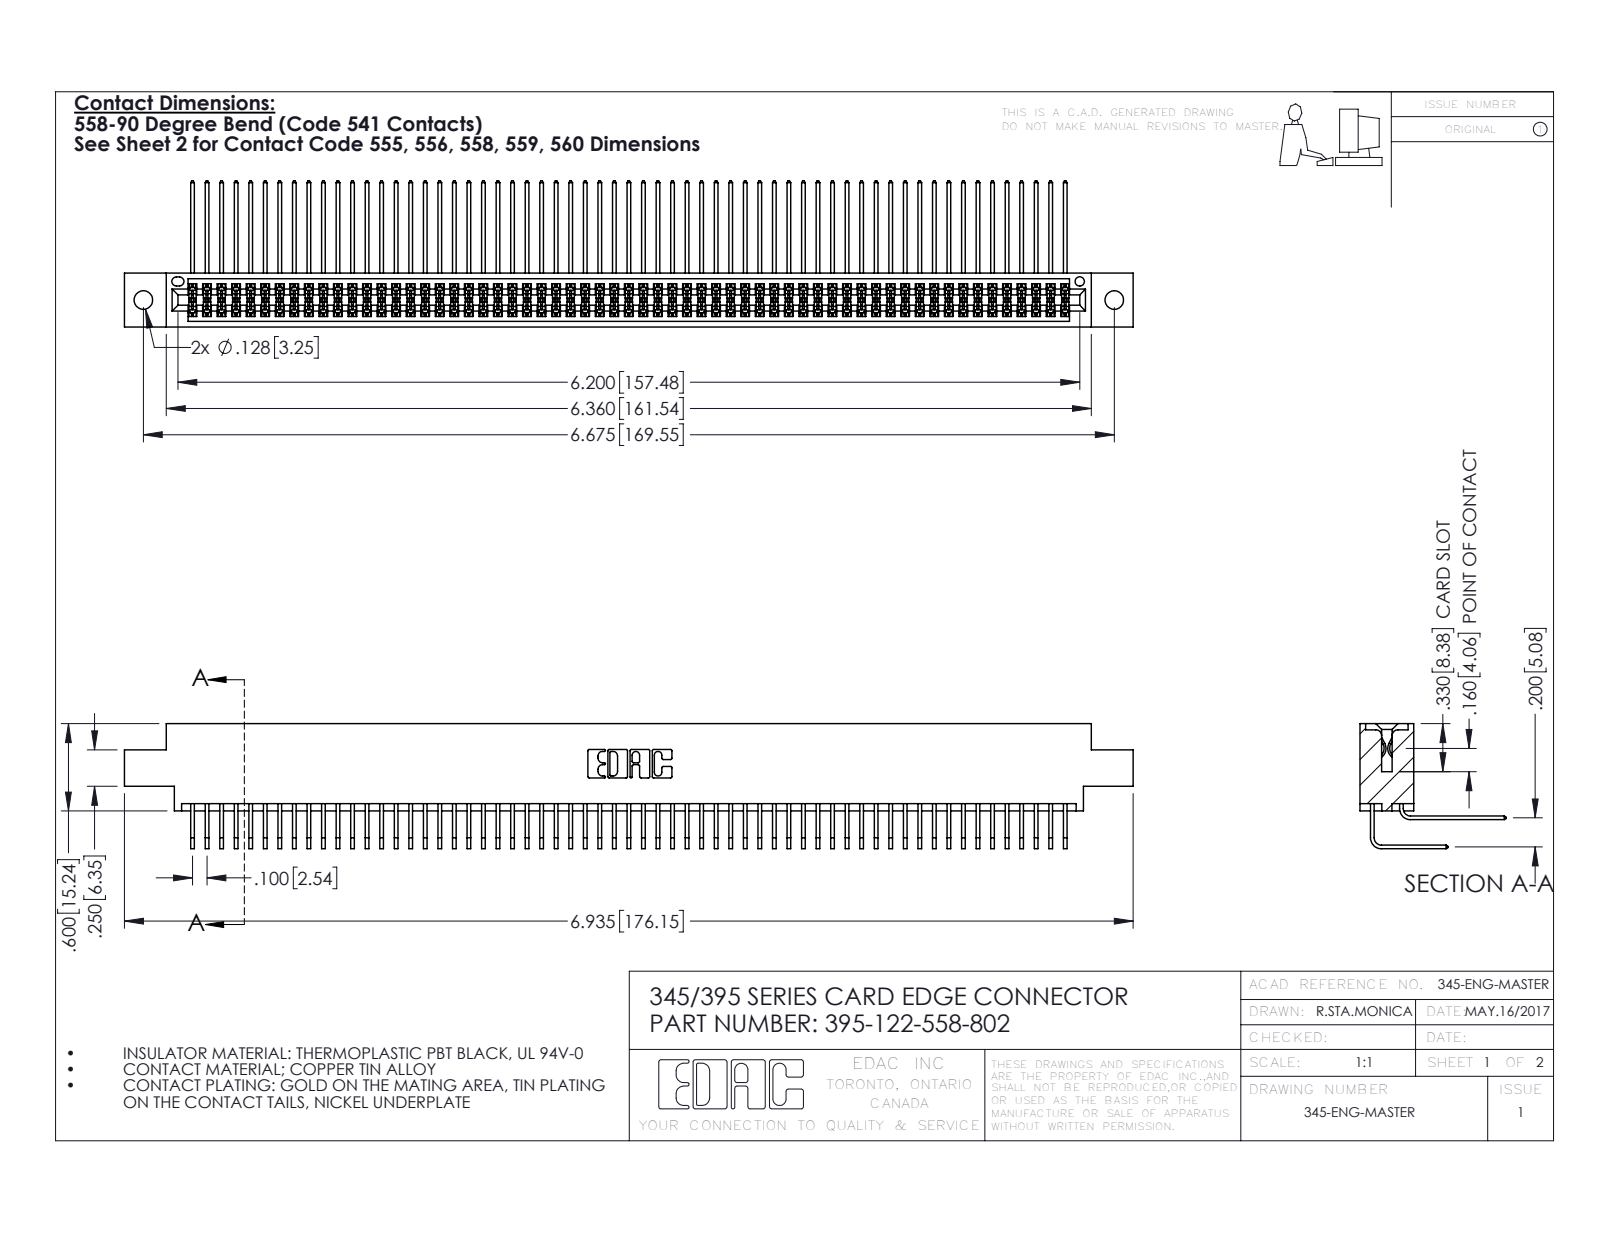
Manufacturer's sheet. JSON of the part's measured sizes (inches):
{"part_name": "395-122-558-802; 345-292-001_558 559 Tail - 1; 345 Part_0.170 Offset - 0.128 Dia; 345-292-001_558 Tail - 2", "step_written_by": "SolidWorks 2016 (CONFIG_CONTROL_DESIGN)", "units": "inches", "bodies": {"solids": 123, "faces": 6474, "planar": 4354, "cylindrical": 2120, "other": 0}, "overall_size": [6.935, 1.005, 0.859], "volume_in3": 1.089, "surface_area_in2": 46.38, "round_holes": [[0.128, 2], [0.064, 1]], "partial_cylinders_radius": [[0.006, 183], [0.01, 22], [0.007, 6], [0.031, 6], [0.026, 3], [0.014, 2], [0.019, 2], [0.022, 2]], "face_to_face_distances": [0.072, 0.298, 0.2, 0.37, 0.098, 0.272, 0.025, 0.225, 0.175, 0.025], "hole_center_spacings": [0.27, 6.439, 6.675]}
